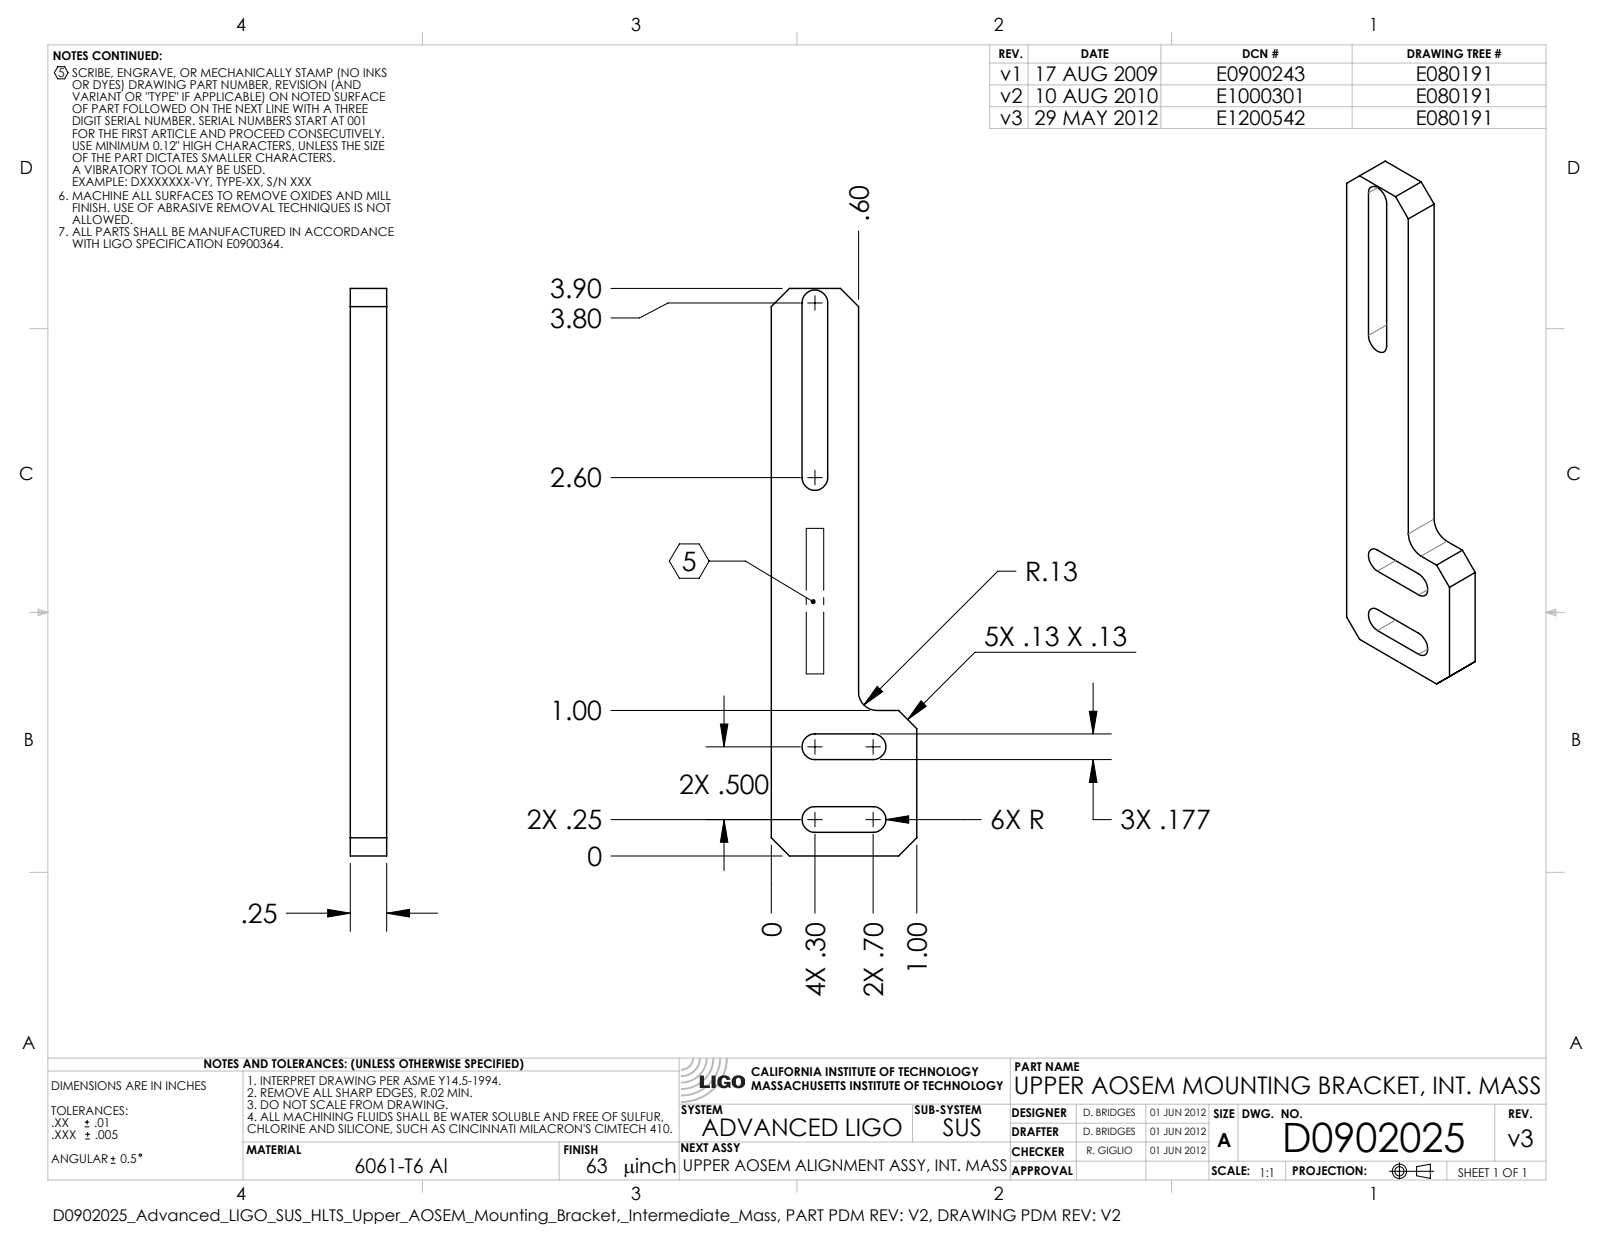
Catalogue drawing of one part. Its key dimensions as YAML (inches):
part_name: "D0902025-v3"
step_written_by: "SolidWorks 2012 (CONFIG_CONTROL_DESIGN)"
units: inches
bodies: {solids: 1, faces: 28, planar: 19, cylindrical: 9, other: 0}
overall_size: [3.9, 1, 0.25]
volume: 0.569
surface_area: 8.315
partial_cylinders:
  - {radius: 0.089, count: 6}
  - {radius: 0.125, count: 1}
face_to_face_distances: [0.25, 0.6, 0.211, 0.389, 0.177, 1, 0.5, 0.789, 0.611, 0.4]
